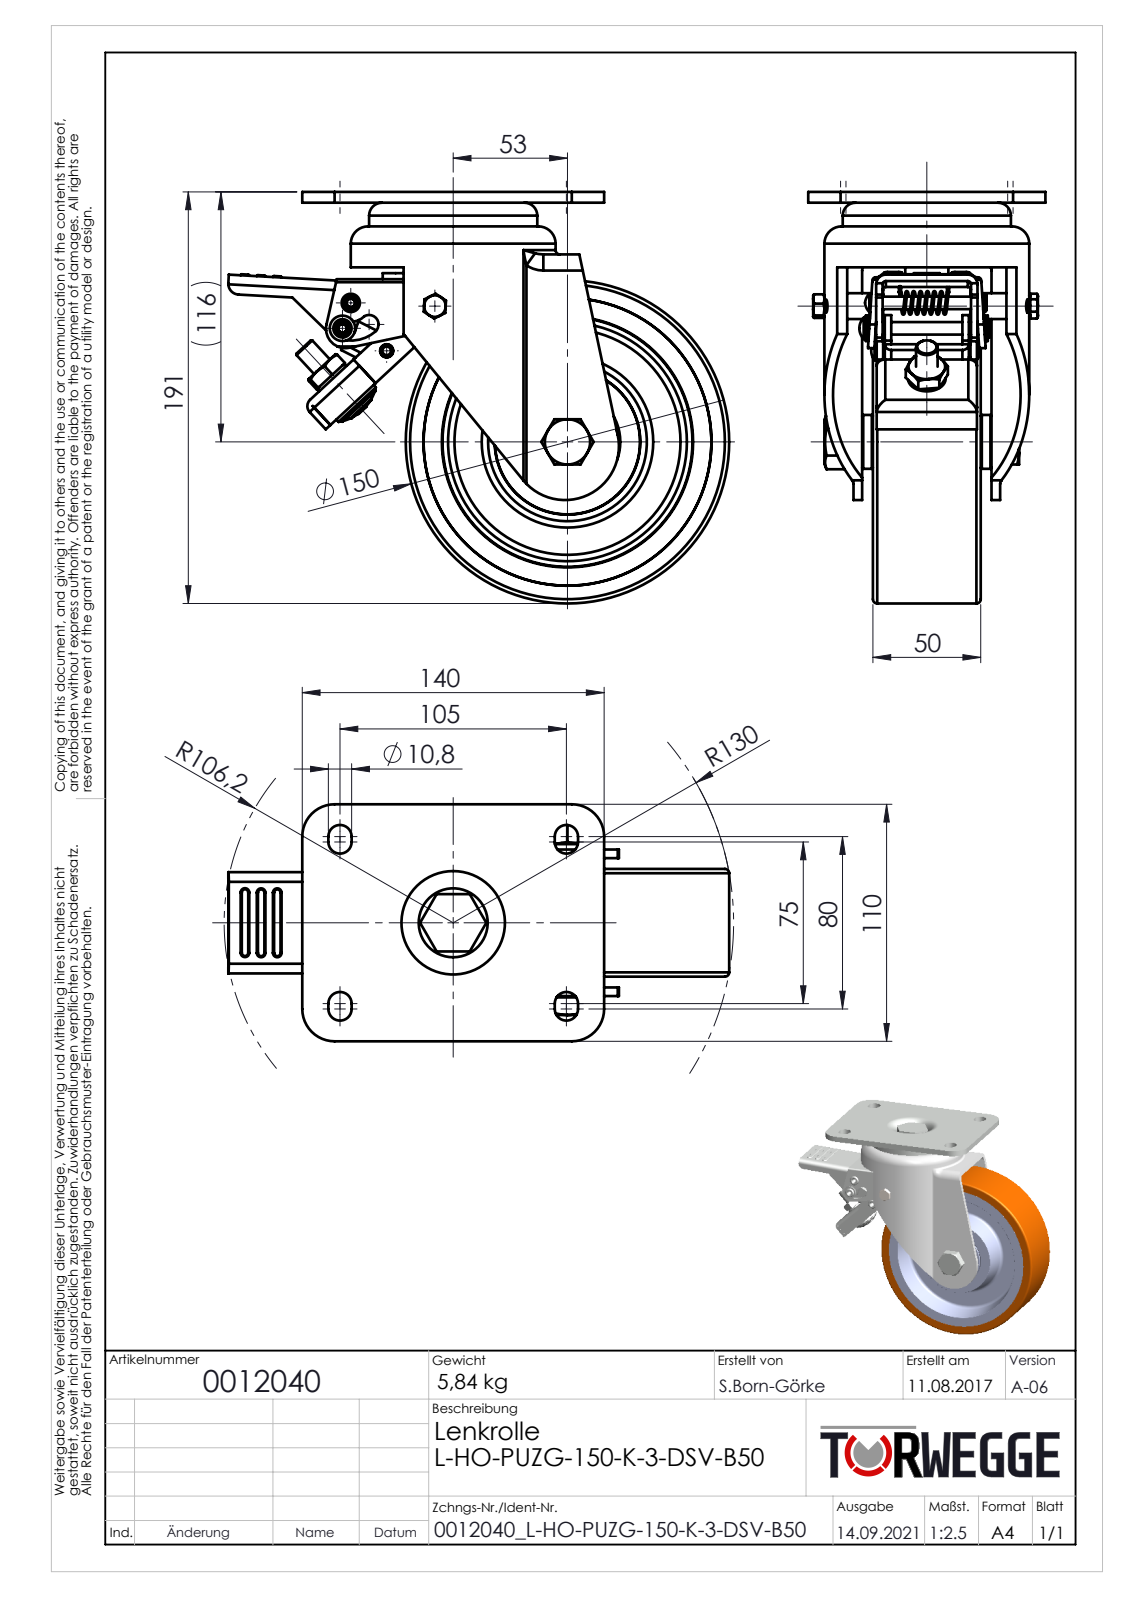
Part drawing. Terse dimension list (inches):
name: 0012040
written by: SolidWorks 2020 (AUTOMOTIVE_DESIGN)
unit: in
bodies: 0 solids, 697 faces (239 planar, 234 cylindrical, 224 other)
size: 9.145 × 7.52 × 4.429
holes: 4× ⌀0.236, 2× ⌀0.33, 1× ⌀0.157, 1× ⌀0.197, 1× ⌀0.228, 1× ⌀0.244, 1× ⌀0.248, 1× ⌀0.315, 1× ⌀0.331, 1× ⌀0.466, 1× ⌀0.559, 1× ⌀0.571
bosses: 2× ⌀0.787, 2× ⌀0.472, 2× ⌀0.394, 2× ⌀0.039, 1× ⌀5.906, 1× ⌀3.74, 1× ⌀3.071, 1× ⌀1.85
rounds: 16× R0.059, 8× R0.213, 6× R0.02, 4× R0.039, 4× R0.591, 3× R0.157, 3× R0.295, 2× R0.079
face distances: 0.197, 0.157, 0.787, 1.969, 0.63, 1.181, 0.433, 0.984, 0.354, 1.142
hole spacings: 0.489, 0.906, 1.094, 1.201, 1.537, 1.735, 3.466, 3.697
